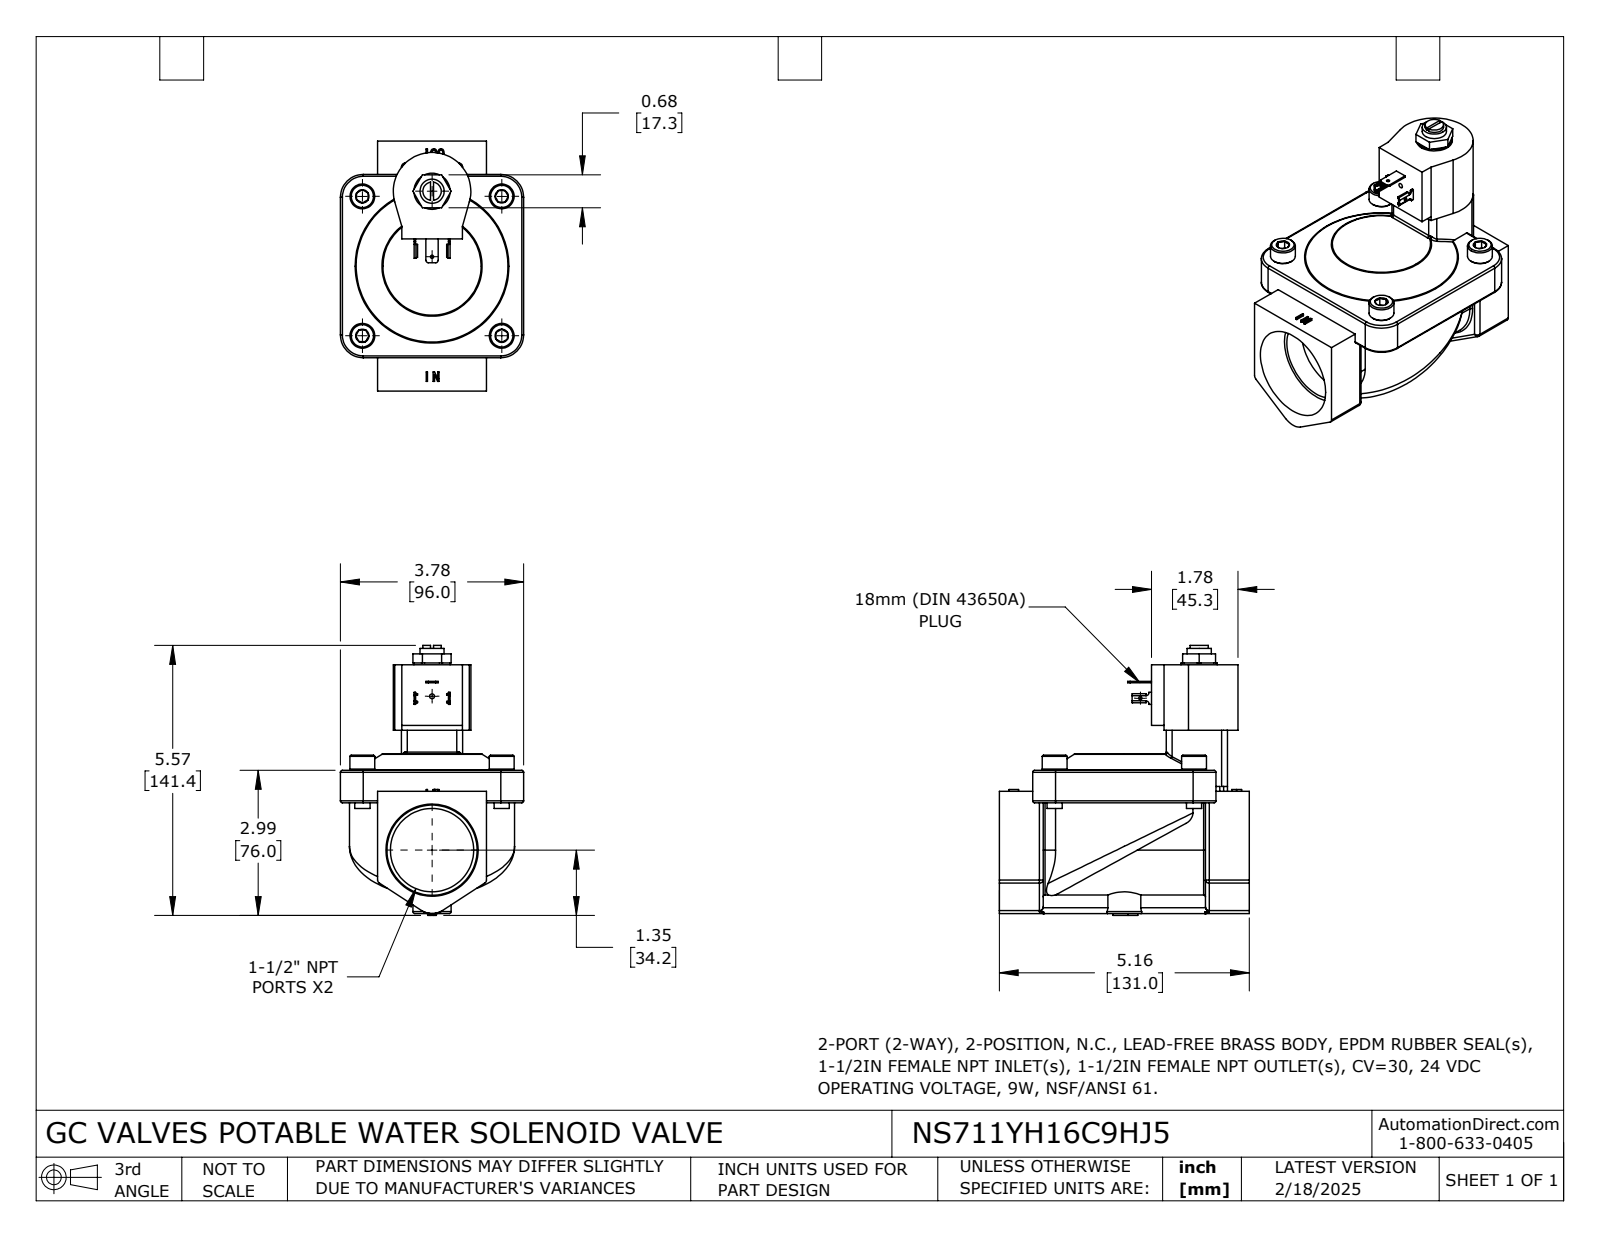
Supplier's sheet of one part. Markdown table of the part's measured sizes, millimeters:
| quantity | value |
| --- | --- |
| part name | NS711YH16C9HJ5 |
| STEP written by | SolidWorks 2024 (CONFIG_CONTROL_DESIGN) |
| units | millimeters |
| bodies | 1 solid, 442 faces (201 planar, 115 cylindrical, 126 other) |
| overall size | 141.37 × 131 × 96 |
| volume | 541 934 mm³ |
| surface area | 70 734 mm² |
| round holes (diameter × count) | 1.68 × 1, 1.7 × 1, 2.53 × 1, 30.48 × 1, 43.66 × 1 |
| round bosses / shafts (diameter × count) | 13 × 4, 8 × 4, 18.95 × 1, 12.67 × 1, 9.65 × 1 |
| partial cylindrical surfaces (radius × count) | 2 × 14, 1 × 13, 3 × 6, 0.15 × 4, 1.04 × 4, 12 × 4, 0.2 × 2, 1.27 × 2 |
| main face-to-face distances | 19.5, 32, 11, 6, 76.5, 8.5, 96, 17, 25.5, 12.5 |
| hole center spacings | 34.29, 80.56 |
